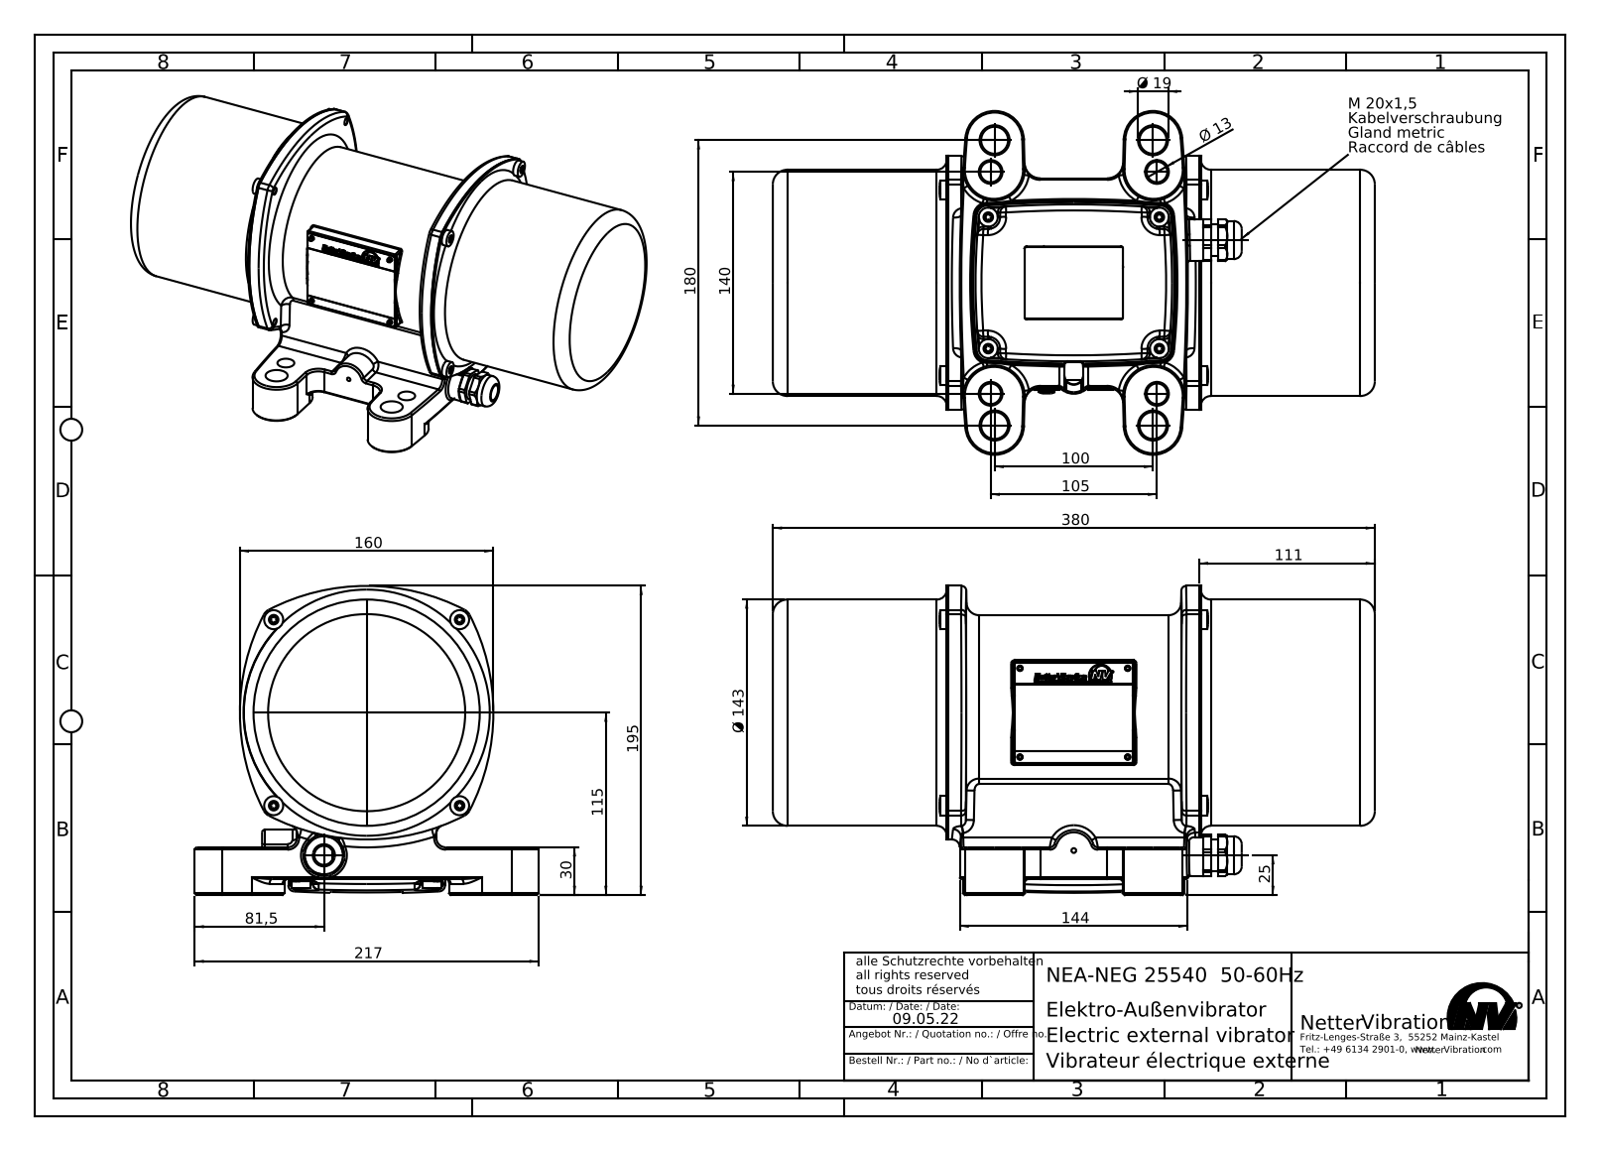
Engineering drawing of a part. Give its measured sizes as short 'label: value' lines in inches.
name: NEA-NEG 25540-50-60Hz
written by: SolidWorks 2015 (AUTOMOTIVE_DESIGN)
unit: in
bodies: 23 solids, 2787 faces (749 planar, 749 cylindrical, 1289 other)
size: 14.961 × 8.543 × 7.677
volume: 92.45 in³; area: 978.3 in²
holes: 4× ⌀0.134, 4× ⌀0.256, 4× ⌀0.276, 4× ⌀0.512, 4× ⌀0.669, 2× ⌀0.472, 2× ⌀0.551, 1× ⌀0.571, 1× ⌀0.728, 1× ⌀4.803, 1× ⌀5.528
bosses: 8× ⌀0.472, 8× ⌀0.236, 3× ⌀0.394, 3× ⌀0.197, 1× ⌀5.622, 1× ⌀0.945, 1× ⌀0.787, 1× ⌀0.63
rounds: 62× R0.079, 34× R0.039, 33× R0.02, 16× R0.059, 14× R0.118, 12× R0.01, 11× R0.069, 11× R0.089
face distances: 0.047, 14.913, 4.323, 10.591, 0.591, 14.961, 14.866, 4.37, 10.543, 0.945
hole spacings: 3.268, 0.794, 1.124, 1.916, 4.111, 4.341, 4.39, 4.518
